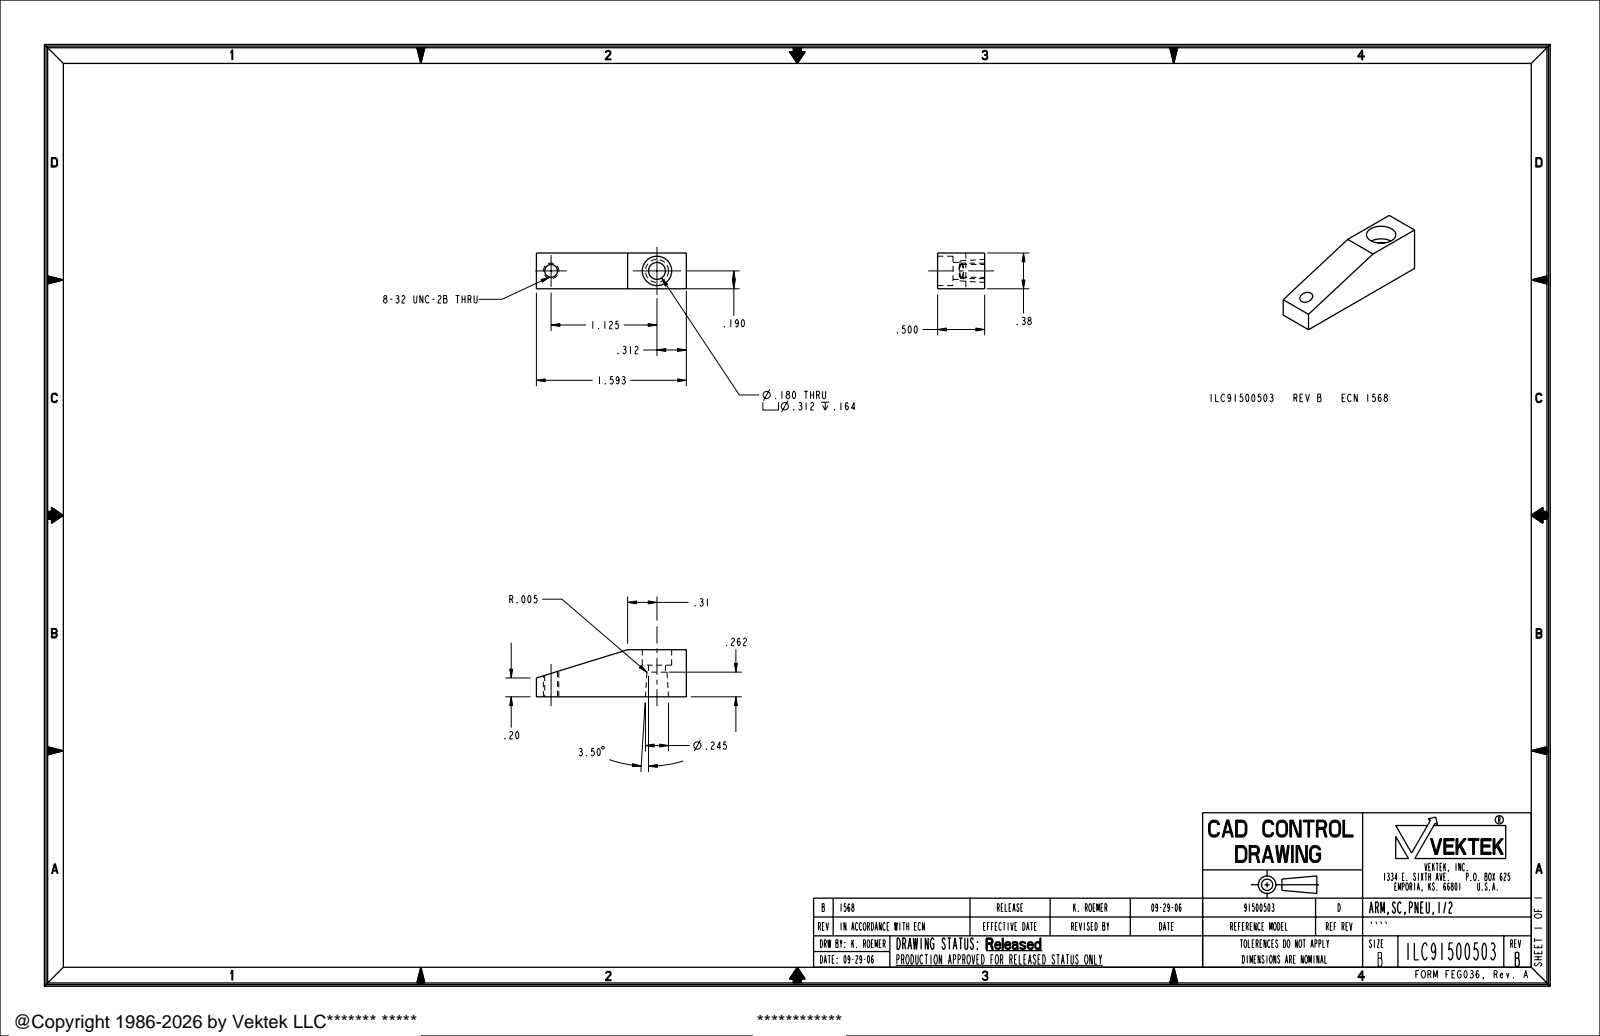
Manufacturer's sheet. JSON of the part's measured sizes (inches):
{"part_name": "ILC91500503", "step_written_by": "PRO/ENGINEER BY PARAMETRIC TECHNOLOGY CORPORATION, 2005180 (AUTOMOTIVE_DESIGN_CC2)", "units": "inches", "bodies": {"solids": 1, "faces": 21, "planar": 9, "cylindrical": 8, "other": 4}, "overall_size": [1.593, 0.5, 0.38], "volume_in3": 0.219, "surface_area_in2": 3.328, "round_holes": [[0.136, 1], [0.18, 1], [0.312, 1]], "round_bosses_or_shafts": [[0.164, 1]], "face_to_face_distances": [0.38, 0.5, 1.593, 0.336, 0.164, 0.262, 0.074, 0.238], "hole_center_spacings": [1.125]}
